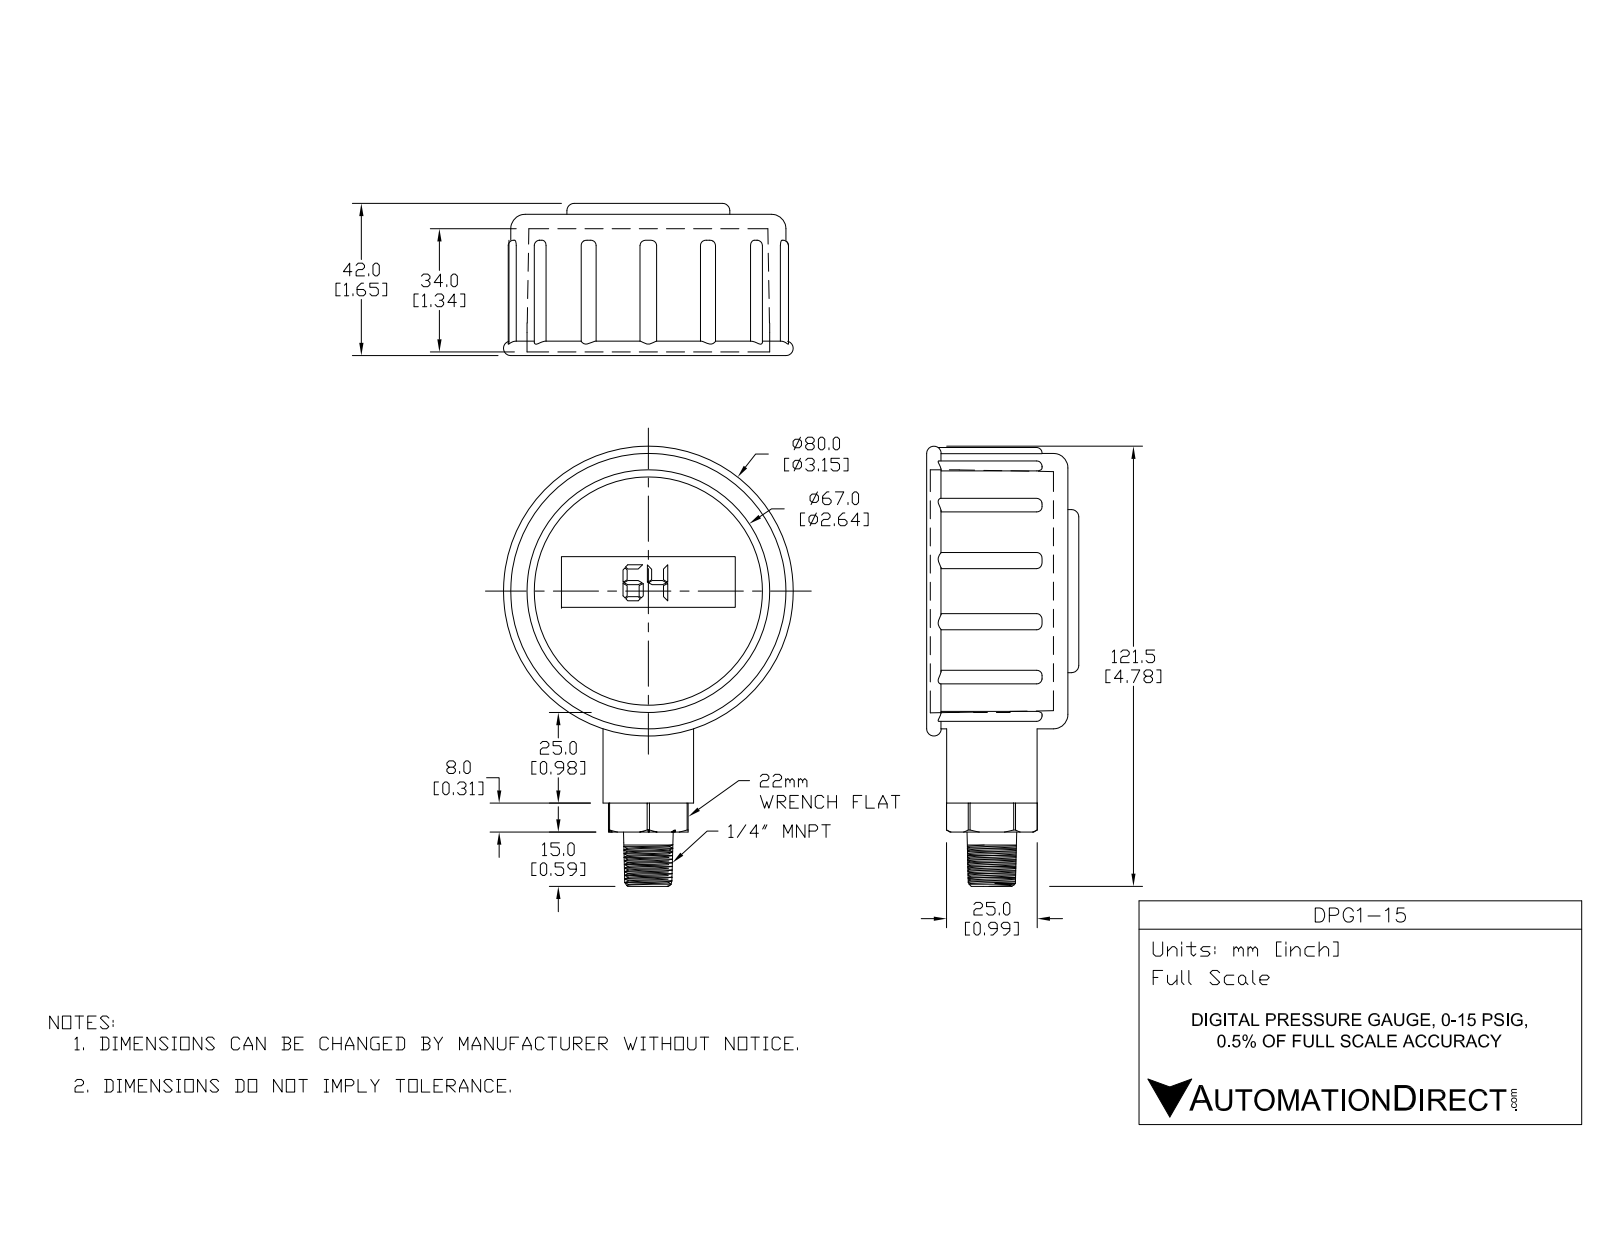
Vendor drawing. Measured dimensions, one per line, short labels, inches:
name: DPG1-15
written by: SolidWorks 2021 (CONFIG_CONTROL_DESIGN)
unit: in
bodies: 4 solids, 181 faces (71 planar, 49 cylindrical, 61 other)
size: 4.788 × 3.15 × 1.654
volume: 11.97 in³; area: 71.27 in²
holes: 1× ⌀2.48, 1× ⌀2.645
bosses: 1× ⌀2.992, 1× ⌀2.638, 1× ⌀1.772, 1× ⌀0.984, 1× ⌀0.394
rounds: 13× R0.094, 6× R0.335, 1× R1.496
face distances: 1.337, 0.157, 1.494, 0.118, 0.276, 1.612, 1.654, 1.535, 1.378, 0.041
